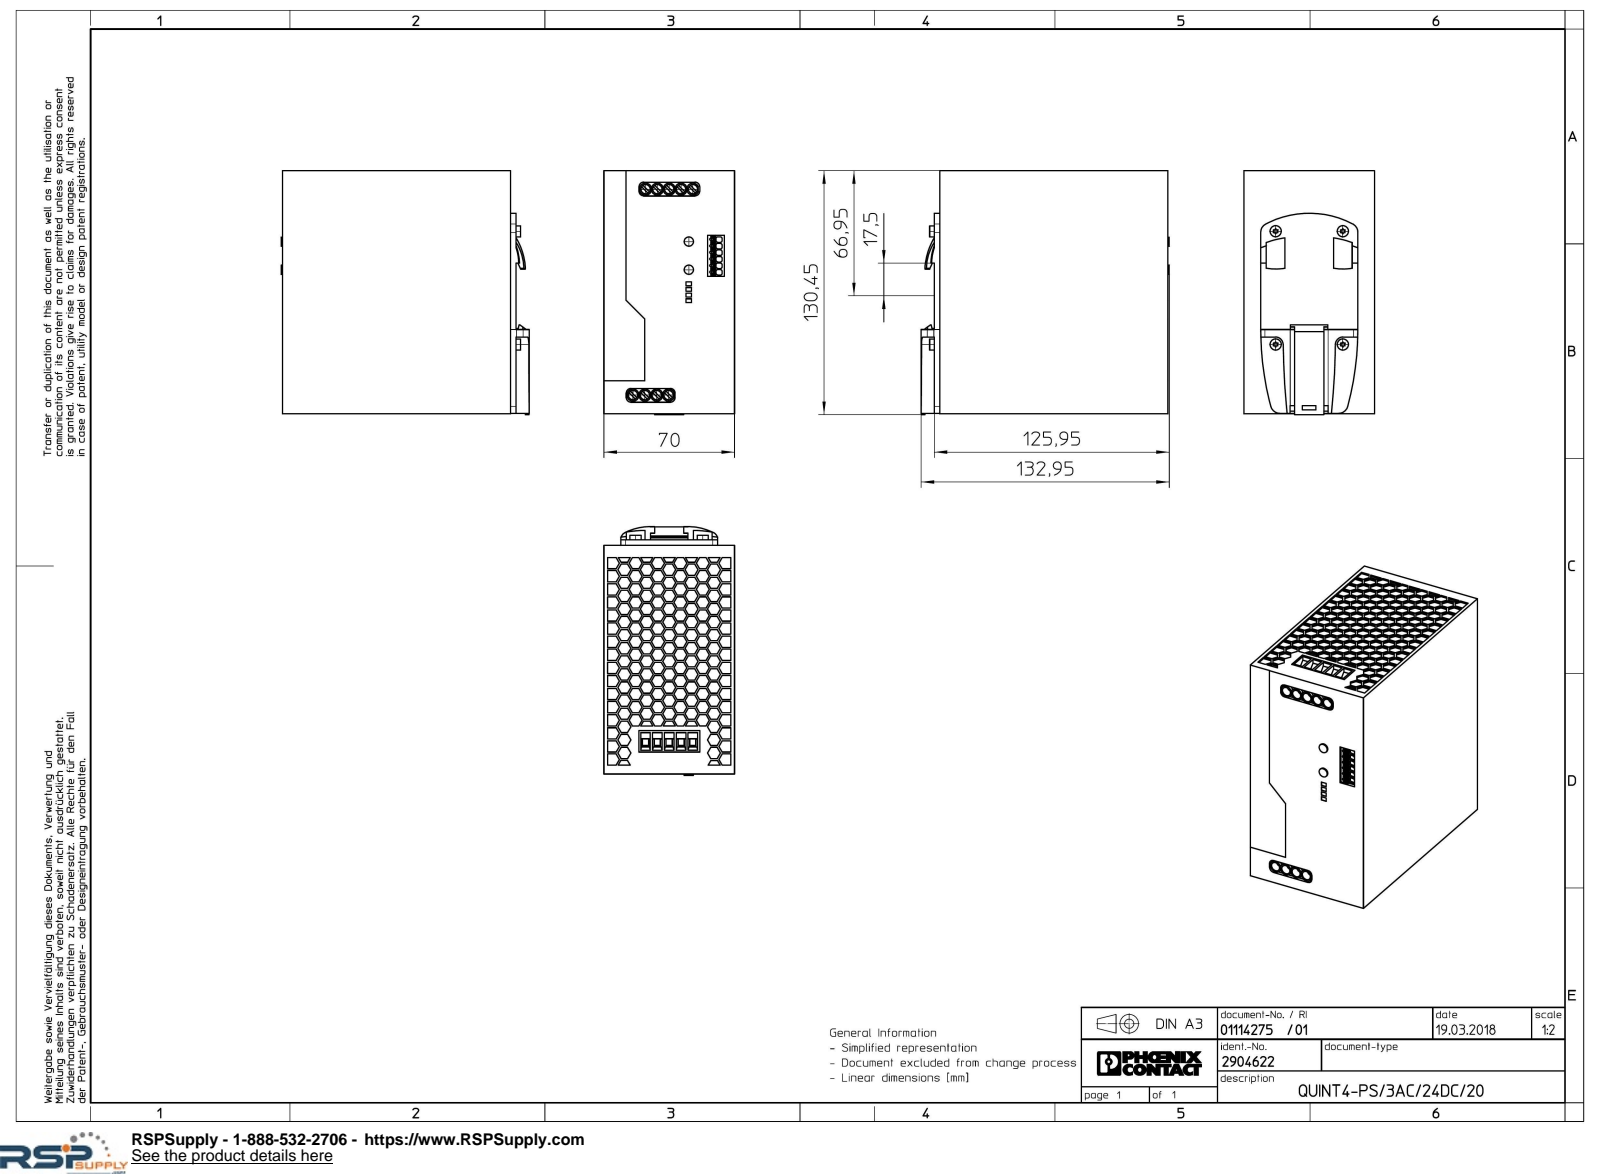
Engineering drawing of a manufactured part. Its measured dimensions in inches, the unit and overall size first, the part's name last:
Units: inches
Overall size (bounding box): 5.234 × 5.136 × 2.756
Round holes (diameter × count): ⌀0.197 ×9
Round bosses / shafts (diameter × count): ⌀0.236 ×4, ⌀0.197 ×2
Partial cylindrical surfaces — rounded edges, fillets, slot ends (radius × count): R0.004 ×48, R0.038 ×12, R0.128 ×9, R0.098 ×8, R0.022 ×6, R0.024 ×6, R0.197 ×4, R0.157 ×2
Main face-to-face distances: 2.756, 0.031, 5.087, 5.055, 4.813, 0.118, 4.931, 5.118, 4.927, 4.809
Hole centre spacings: 0.25, 0.5, 0.75, 1
Volume: 68.65 in³ · Surface area: 122.9 in²
Bodies: 1 solid, 2854 faces (2693 planar, 143 cylindrical, 18 other)
Part name (STEP PRODUCT): QUINT4_PS_3AC_24DC_20-select
STEP written by: Creo Elements/Direct Modeling 20.1A 29-Sep-2018 (C) Parametric Technology GmbH (AUTOMOTIVE_DESIGN)
